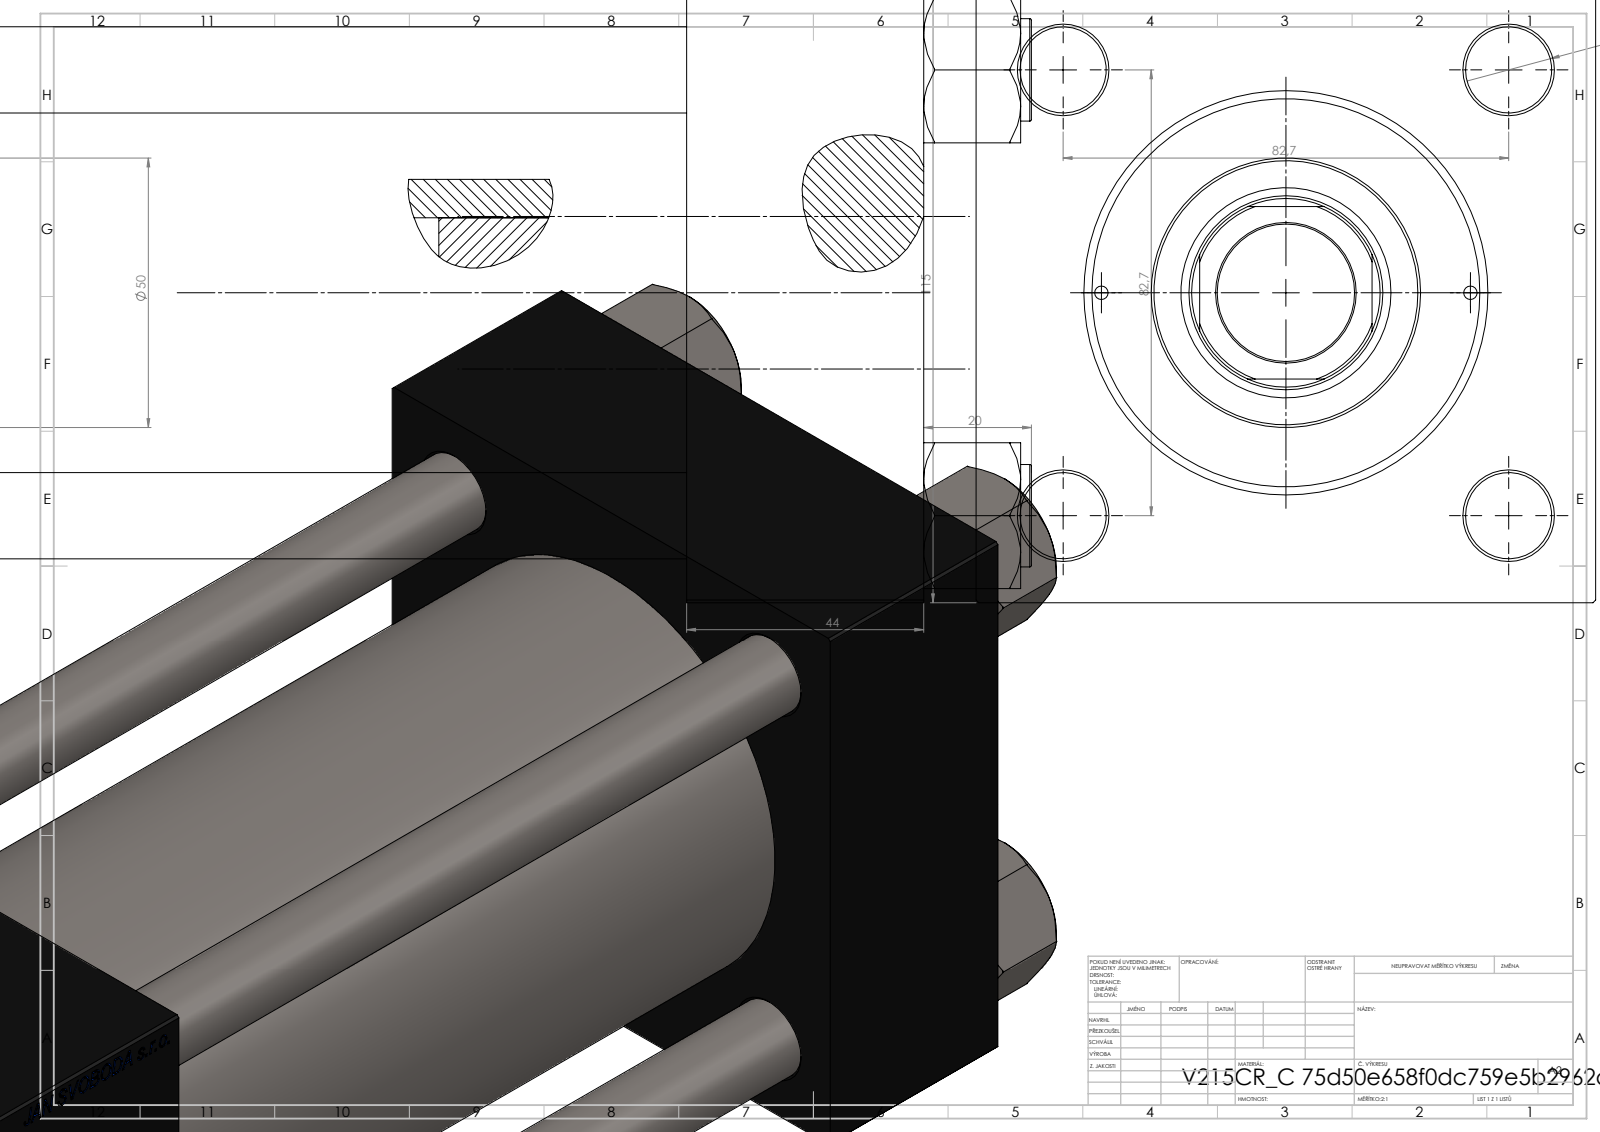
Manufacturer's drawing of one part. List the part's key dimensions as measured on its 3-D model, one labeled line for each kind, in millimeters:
Part name (STEP PRODUCT): V215CR_C_TYCINKA; NUT_M5_C; V215CR_VCP_C; V215_VC_A (+1 more)
STEP written by: SolidWorks 2019 (CONFIG_CONTROL_DESIGN)
Units: millimetres
Bodies: 11 solids, 1202 faces (576 planar, 90 cylindrical, 536 other)
Overall size (bounding box): 335 × 115 × 115
Volume: 2 060 000 mm³ · Surface area: 356 256 mm²
Round holes (diameter × count): ⌀16 ×4, ⌀2.5 ×2, ⌀7 ×2, ⌀26.44 ×2, ⌀35 ×2, ⌀25.5 ×1, ⌀36 ×1, ⌀39 ×1, ⌀61 ×1, ⌀72 ×1, ⌀80 ×1
Round bosses / shafts (diameter × count): ⌀19 ×4, ⌀86 ×1, ⌀50 ×1
Partial cylindrical surfaces — rounded edges, fillets, slot ends (radius × count): R17.5 ×1
Main face-to-face distances: 115, 44, 284, 240, 215, 171, 69, 255.3, 211.3, 40.3
Hole centre spacings: 41.96, 58.48, 82.7, 86.17, 34.25, 116.96, 68.5, 216
